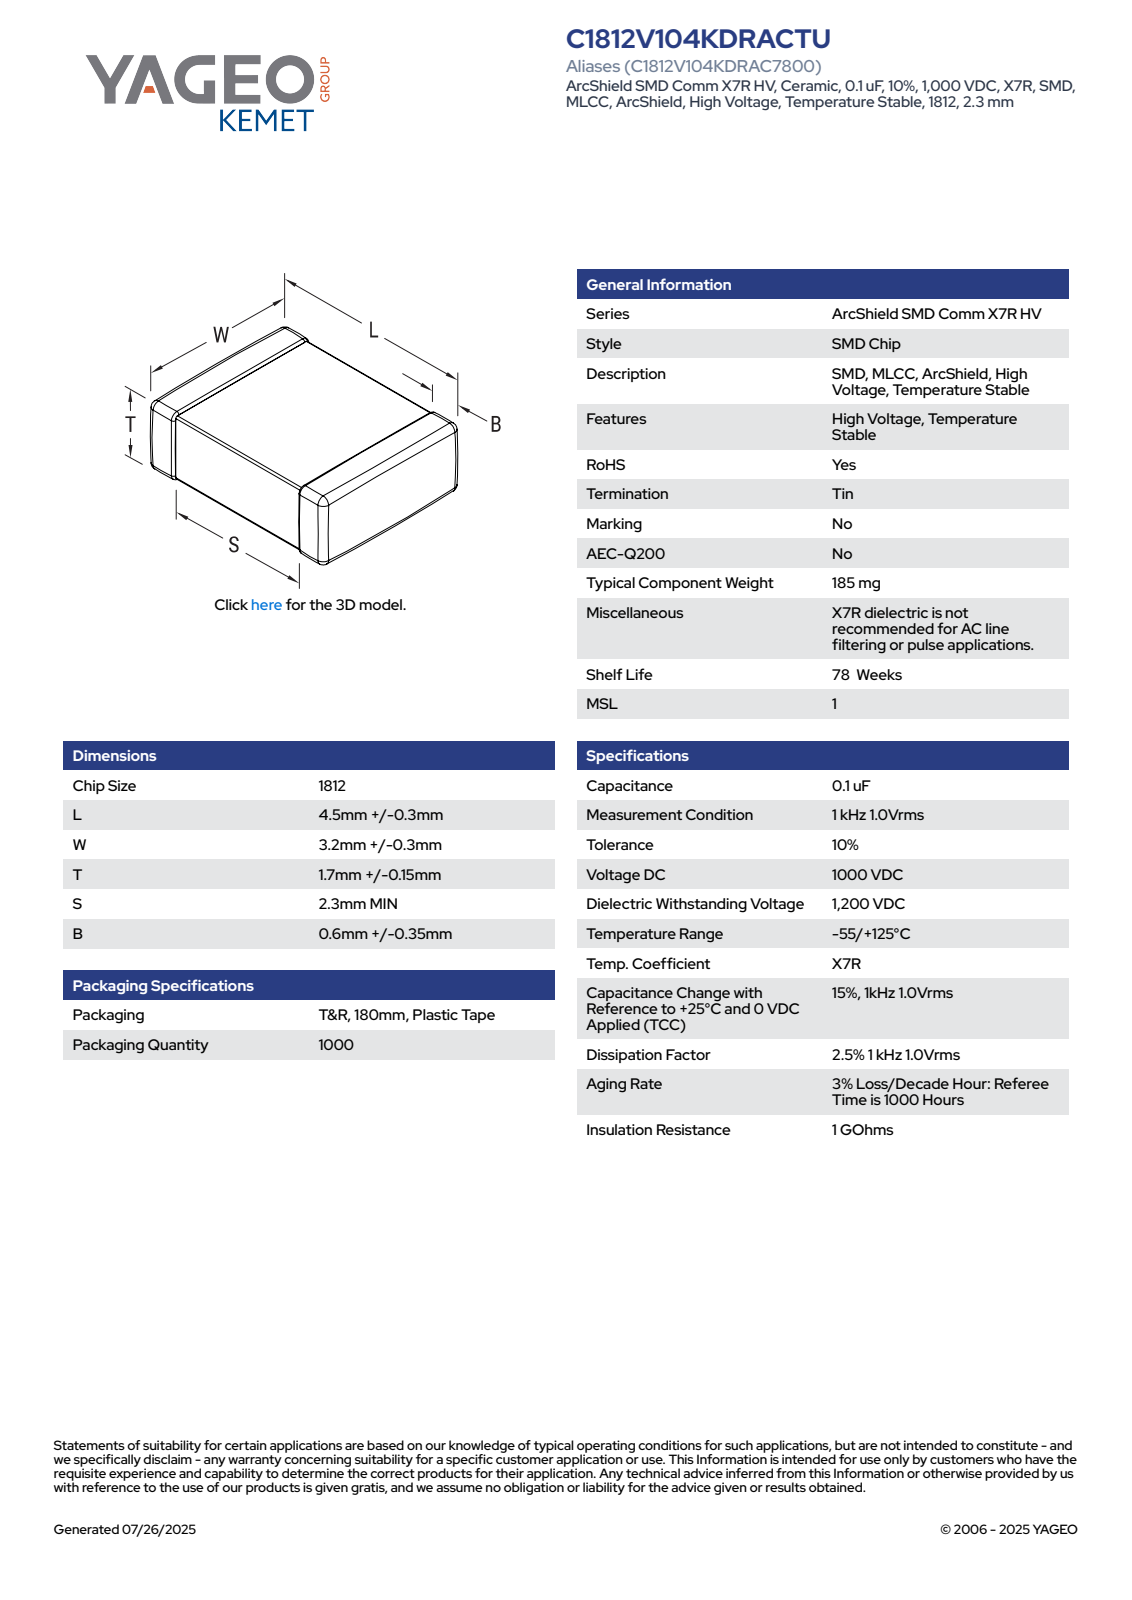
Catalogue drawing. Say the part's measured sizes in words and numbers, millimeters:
The part is named "CCS_CCSTD_1812_L4.8W3.5T1.85B0.6". Its 3-D file was written by "SolidWorks 2021 (AUTOMOTIVE_DESIGN)". It is 4 solids with 129 faces: 71 planar, 42 cylindrical and 16 other. Overall it measures 4.8 by 3.5 by 1.85 millimeters. Its volume is 29 cubic millimeters and its surface area 64 square millimeters. The main face-to-face distances are 1.78, 1.71, 4.8, 3.43, 1.85, 3.36, 3.5, 2.08, 2.72, 2.59.
